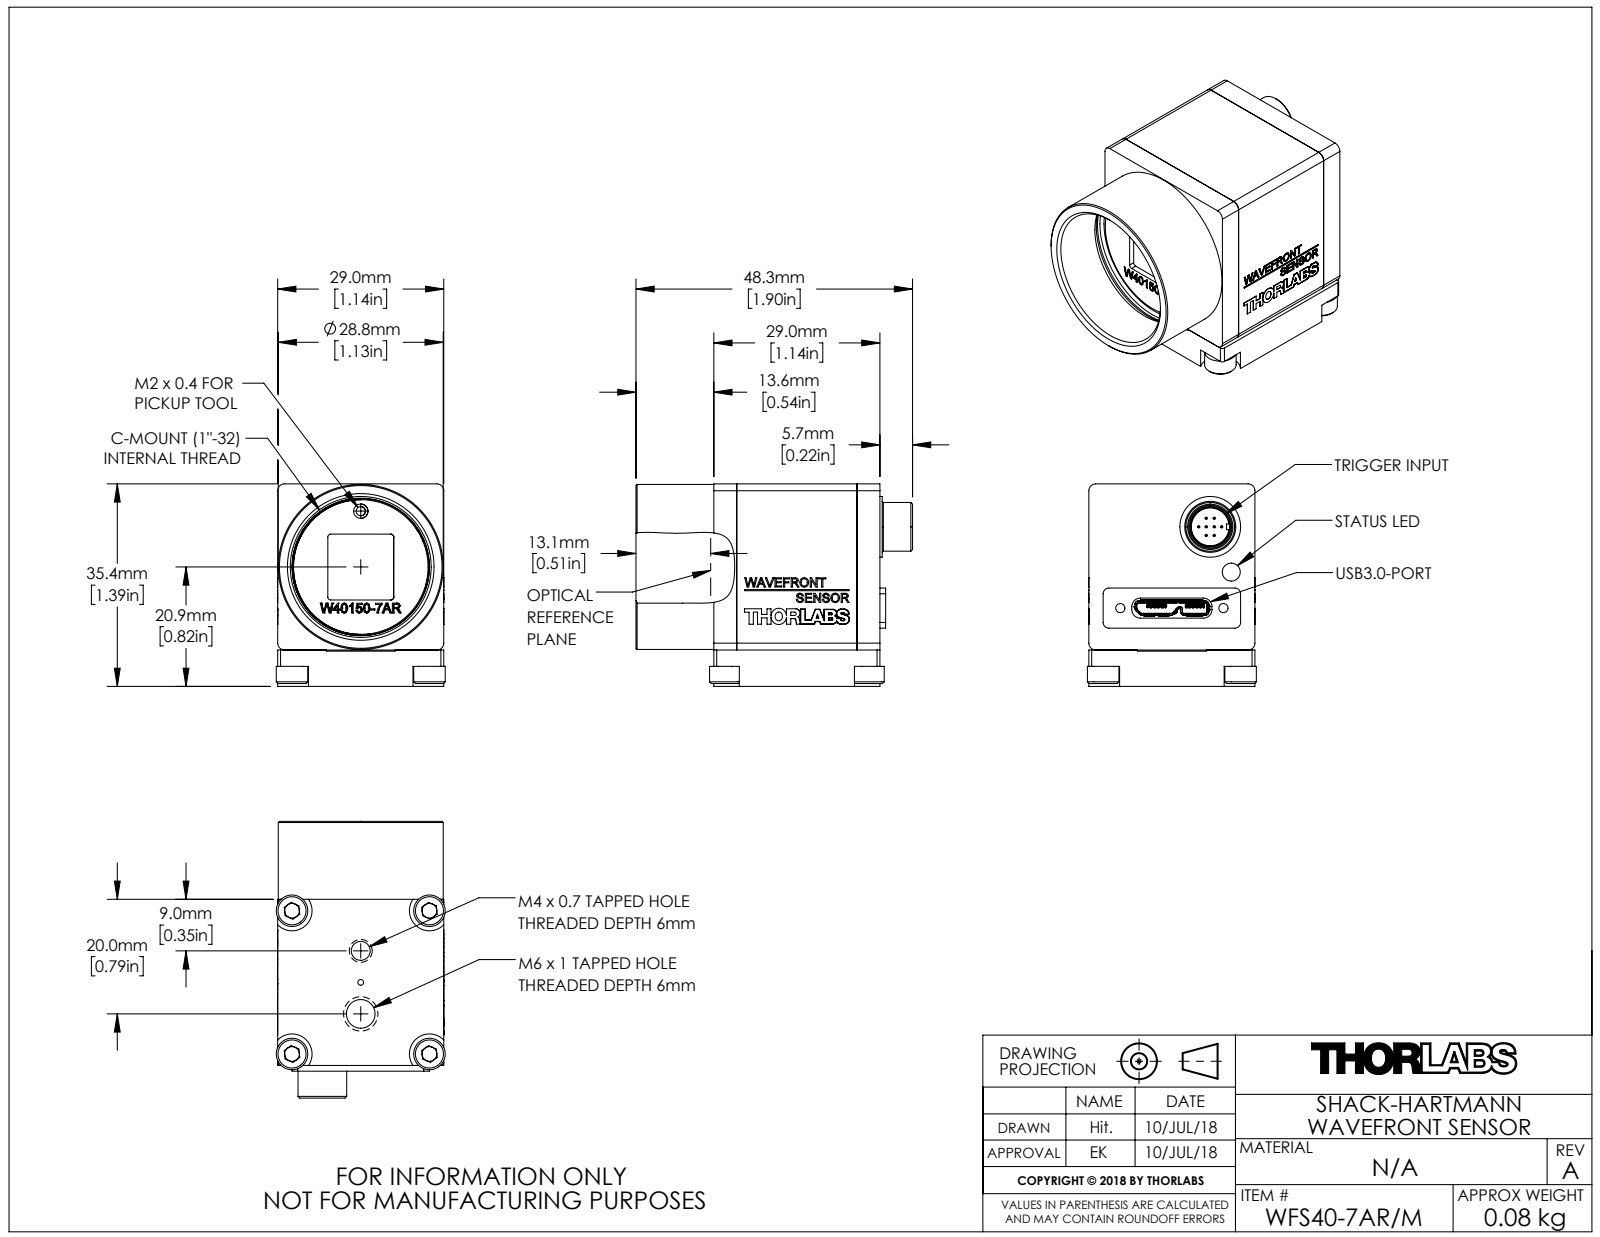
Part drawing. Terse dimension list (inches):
name: MTN008541-E0W
written by: SolidWorks 2016 (AUTOMOTIVE_DESIGN)
unit: in
bodies: 0 solids, 2619 faces (1899 planar, 413 cylindrical, 307 other)
size: 1.902 × 1.392 × 1.161
holes: 10× ⌀0.126, 5× ⌀0.098, 3× ⌀0.063, 3× ⌀0.075, 1× ⌀0.037, 1× ⌀0.039, 1× ⌀0.059, 1× ⌀0.13, 1× ⌀0.197, 1× ⌀0.268, 1× ⌀0.315, 1× ⌀0.591
bosses: 8× ⌀0.016, 6× ⌀0.039, 5× ⌀0.118, 4× ⌀0.217, 1× ⌀1.134, 1× ⌀0.941, 1× ⌀0.925, 1× ⌀0.417
rounds: 37× R0.02, 31× R0.008, 29× R0.006, 15× R0.039, 12× R0.012, 10× R0.059, 8× R0.004, 8× R0.024
face distances: 0.024, 1.142, 1.118, 0.25, 0.039, 0.656, 1.392, 0.047, 0.189, 1.094
hole spacings: 0.384, 0.665, 0.383, 0.199, 0.543, 0.741, 0.547, 0.682
